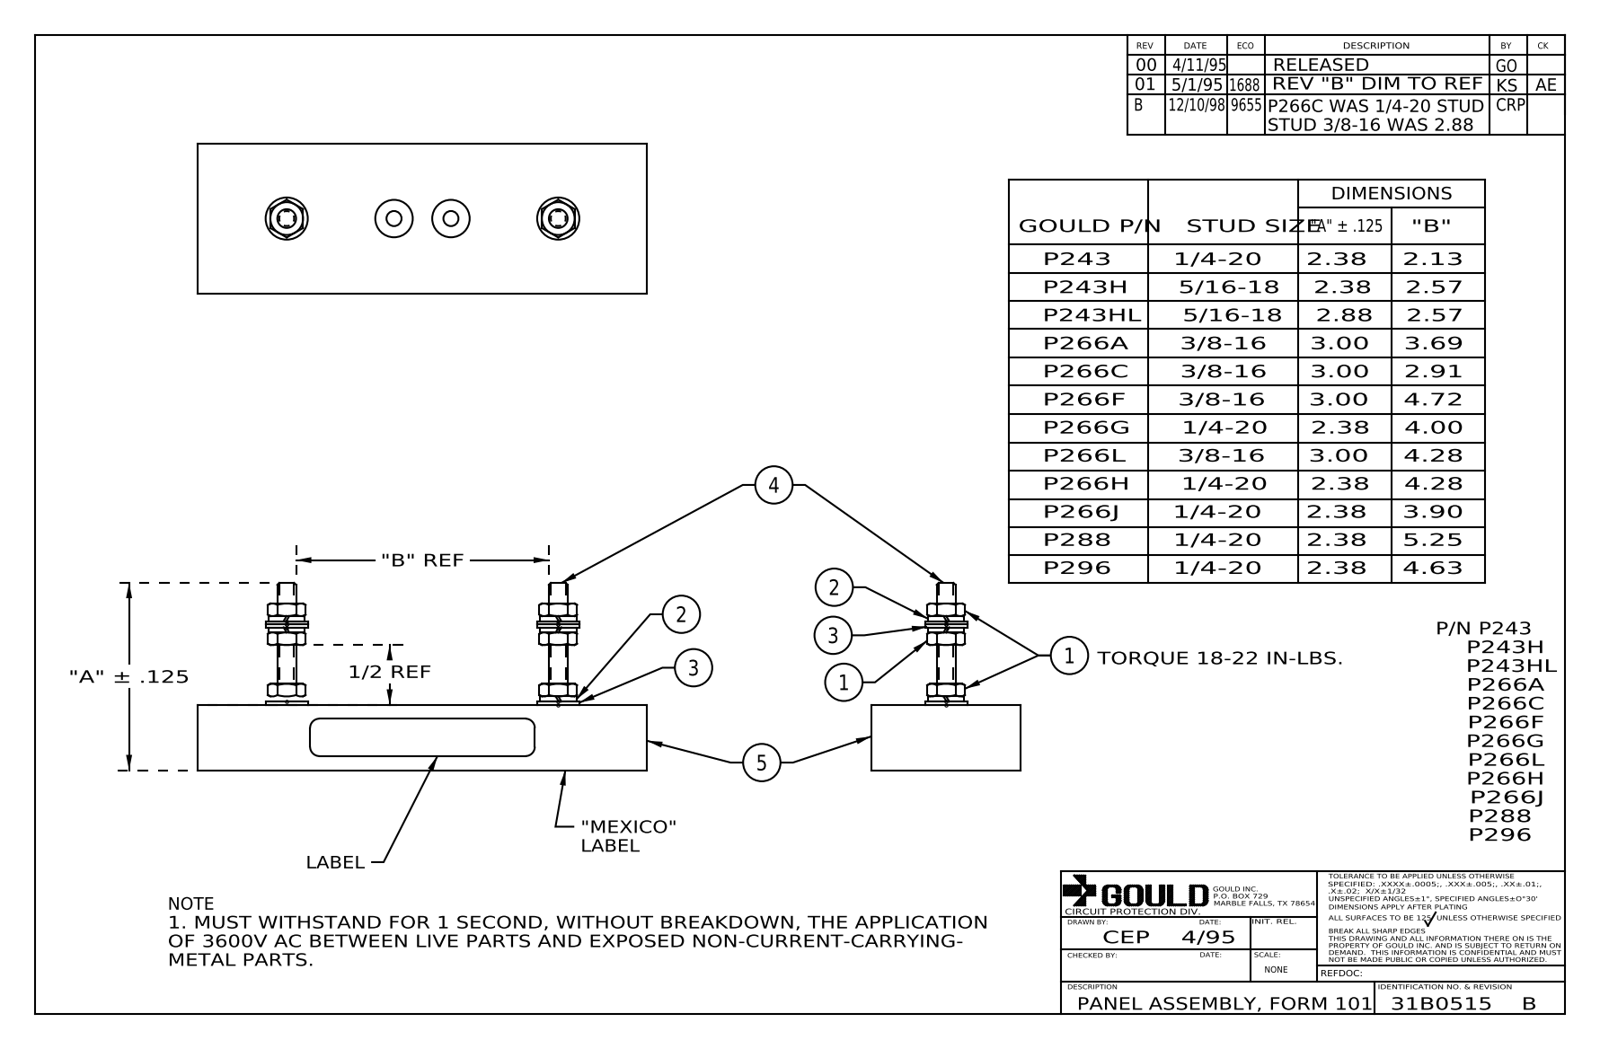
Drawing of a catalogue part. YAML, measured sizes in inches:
part_name: "16425revn"
step_written_by: "SolidWorks 2012 (AUTOMOTIVE_DESIGN)"
units: inches
bodies: {solids: 21, faces: 582, planar: 84, cylindrical: 356, other: 142}
overall_size: [6, 3, 2]
volume: 11.32
surface_area: 71.8
round_holes:
  - {diameter: 0.201, count: 2}
  - {diameter: 0.294, count: 2}
  - {diameter: 0.313, count: 2}
  - {diameter: 0.38, count: 2}
  - {diameter: 0.406, count: 2}
  - {diameter: 0.5, count: 2}
  - {diameter: 0.375, count: 1}
round_bosses_or_shafts:
  - {diameter: 0.812, count: 2}
  - {diameter: 0.68, count: 2}
  - {diameter: 0.375, count: 2}
face_to_face_distances: [0.88, 2, 1.403, 6, 2.283, 0.065, 0.563, 0.526, 0.263, 0.328]
hole_center_spacings: [1.65, 2.41, 0.76, 4.06]
